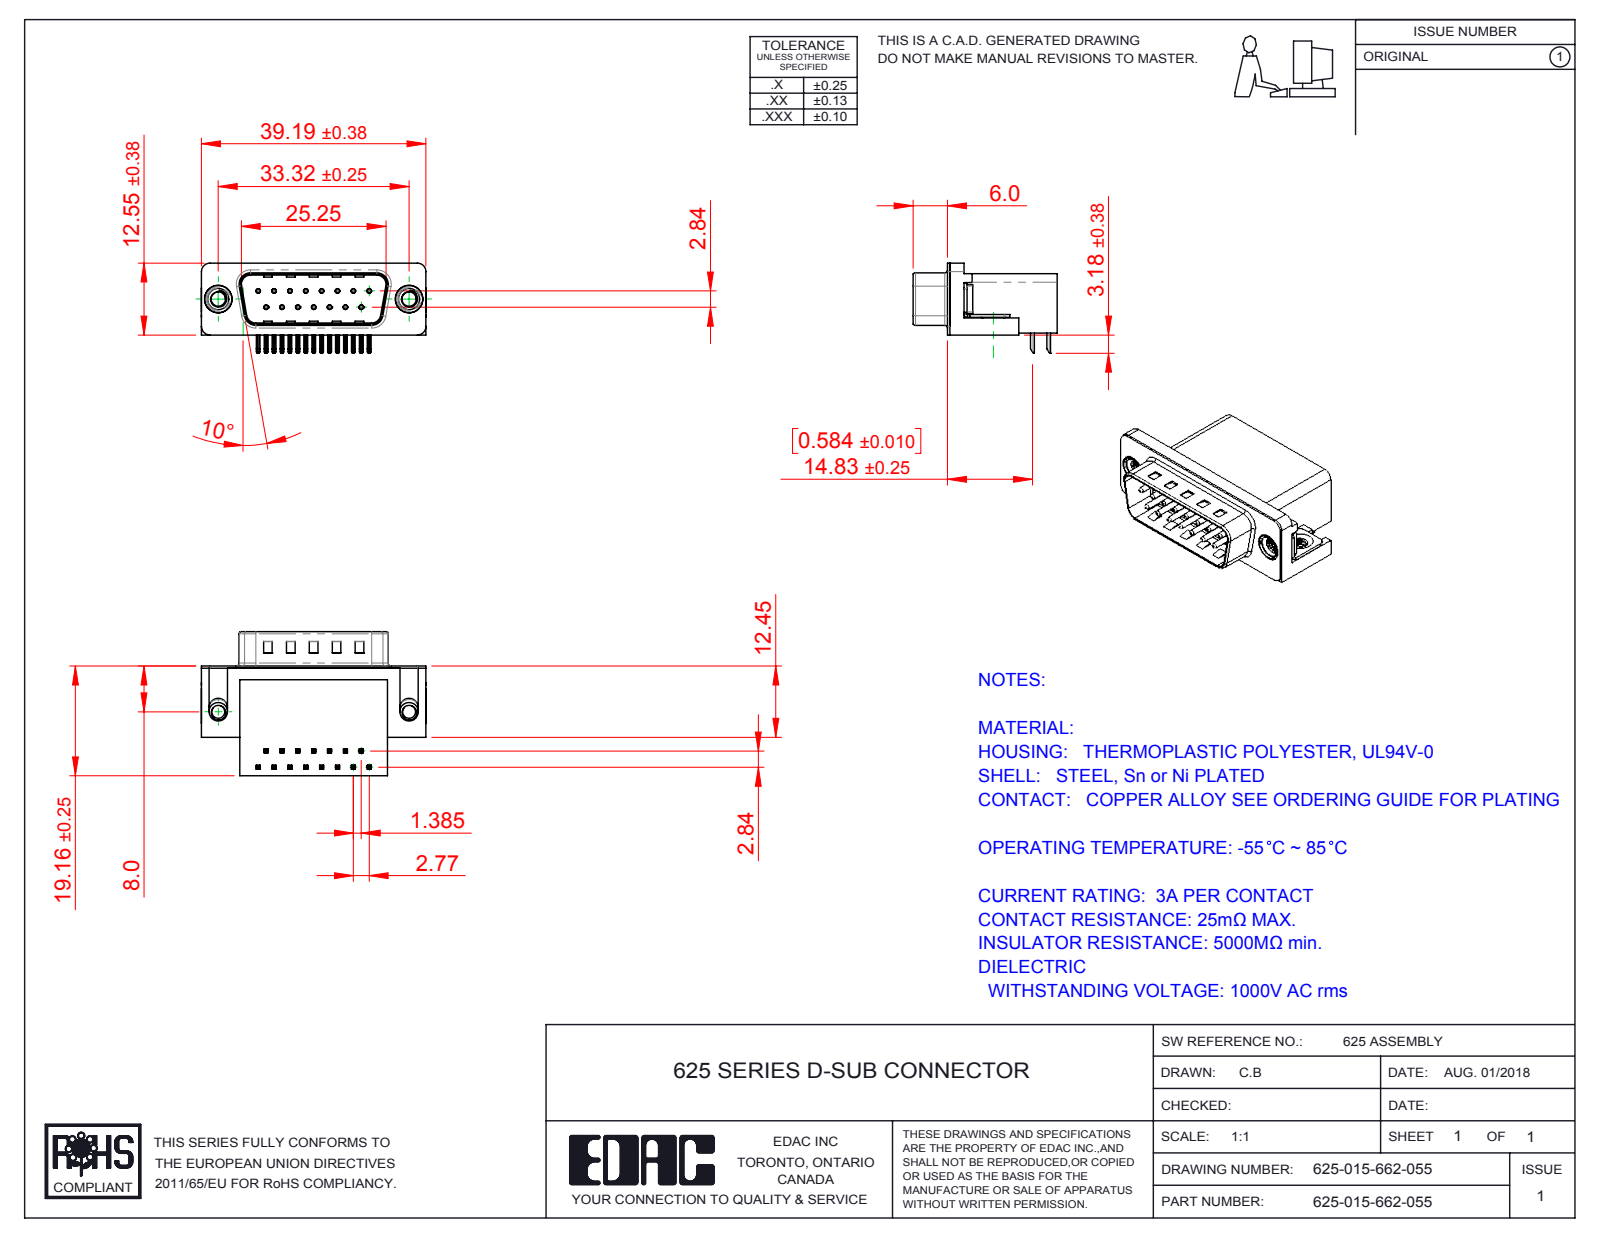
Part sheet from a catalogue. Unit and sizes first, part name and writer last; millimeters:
Units: millimetres
Overall size (bounding box): 39.22 × 25.16 × 15.73
Round holes (diameter × count): ⌀0.35 ×15, ⌀0.8 ×15, ⌀2.26 ×2, ⌀2.5 ×2, ⌀4 ×2, ⌀4.8 ×2, ⌀5 ×2
Round bosses / shafts (diameter × count): ⌀0.75 ×15, ⌀4.9 ×2, ⌀4.75 ×2, ⌀3.9 ×2, ⌀3.26 ×2
Partial cylindrical surfaces — rounded edges, fillets, slot ends (radius × count): R0.25 ×68, R0.12 ×30, R1 ×16, R0.5 ×9, R1.6 ×8, R1.5 ×6, R0.9 ×4, R2 ×4
Main face-to-face distances: 0.4, 10.35, 18.76, 2.1, 10.46, 19.16, 1.7, 10.86, 8.76, 16.26
Hole centre spacings: 3.16, 2.77, 5.54, 8.31, 11.08, 5.03, 5.04, 7.48
Volume: 6 248 mm³ · Surface area: 6 507 mm²
Bodies: 21 solids, 1511 faces (895 planar, 463 cylindrical, 153 other)
Part name (STEP PRODUCT): 625 Housing_15 Socket; 625 Contact Bottom; 625 M3 Threaded Rivet; 625 Shell_15 Socket (+3 more)
STEP written by: SolidWorks 2016 (CONFIG_CONTROL_DESIGN)
